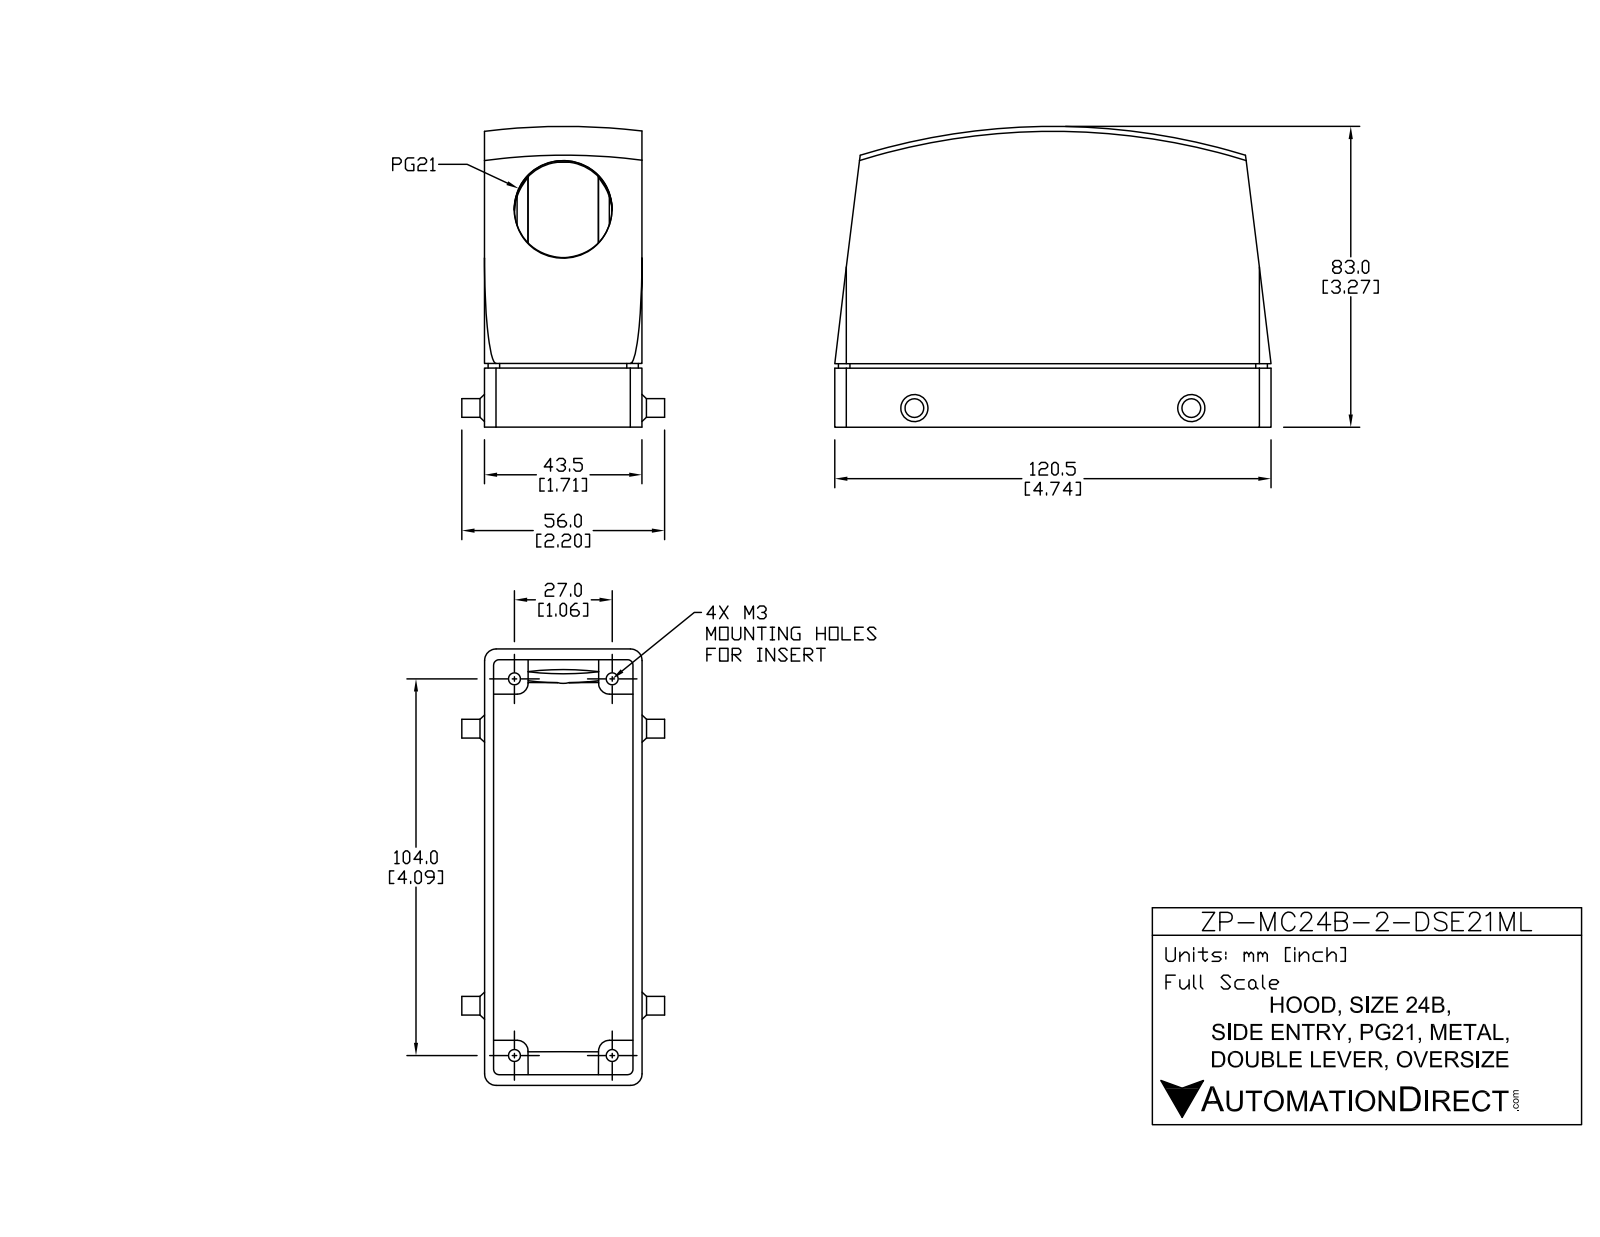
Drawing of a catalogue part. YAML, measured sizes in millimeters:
part_name: "ZP-MC24B-2-DSE21ML"
step_written_by: "SolidWorks 2011 (CONFIG_CONTROL_DESIGN)"
units: millimeters
bodies: {solids: 9, faces: 104, planar: 60, cylindrical: 34, other: 10}
overall_size: [120.5, 77.55, 56]
volume: 79274
surface_area: 61780
round_holes:
  - {diameter: 3.3, count: 4}
  - {diameter: 27, count: 1}
round_bosses_or_shafts:
  - {diameter: 5.17, count: 2}
partial_cylinders:
  - {radius: 3.2, count: 8}
  - {radius: 1.5, count: 4}
  - {radius: 3, count: 4}
  - {radius: 0.7, count: 1}
face_to_face_distances: [2.5, 41, 43.5, 38.5, 9.5, 105.08, 2.96, 12.46, 108.04, 117.54]
hole_center_spacings: [27, 104, 107.45]
